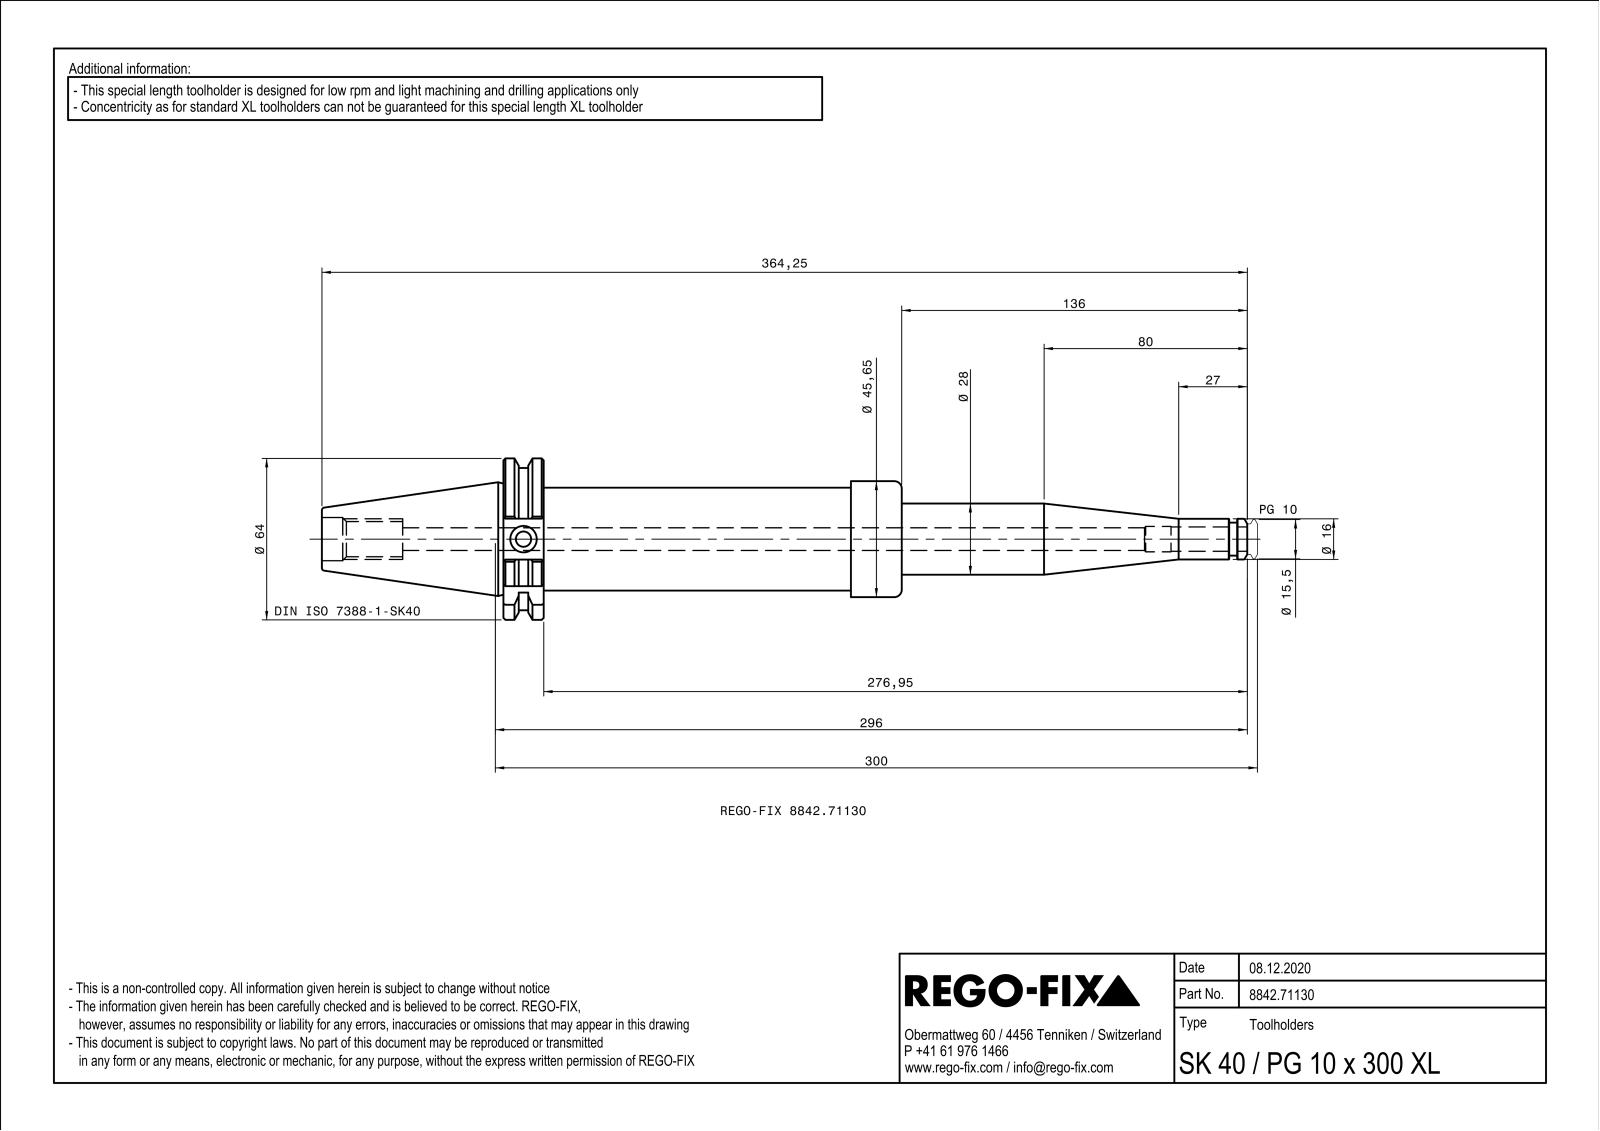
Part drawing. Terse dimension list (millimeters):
name: NOCUT
written by: SIEMENS PLM Software Solid Edge ST10 (AUTOMOTIVE_DESIGN)
unit: mm
bodies: 1 solid, 177 faces (56 planar, 49 cylindrical, 72 other)
size: 364.25 × 63.55 × 61.01
volume: 310 263 mm³; area: 65 354 mm²
holes: 2× ⌀10, 1× ⌀6, 1× ⌀9, 1× ⌀13.84, 1× ⌀17, 1× ⌀25, 1× ⌀29, 1× ⌀38.38, 1× ⌀40.05, 1× ⌀43.3
bosses: 1× ⌀45.65, 1× ⌀40.5, 1× ⌀40, 1× ⌀34, 1× ⌀33, 1× ⌀28, 1× ⌀24.7, 1× ⌀23.8
rounds: 13× R0.5, 1× R22.77, 1× R28, 1× R31.77
face distances: 15.85, 140.95, 156.8, 6, 14, 1.5, 139.45, 155.3, 20, 18.5
